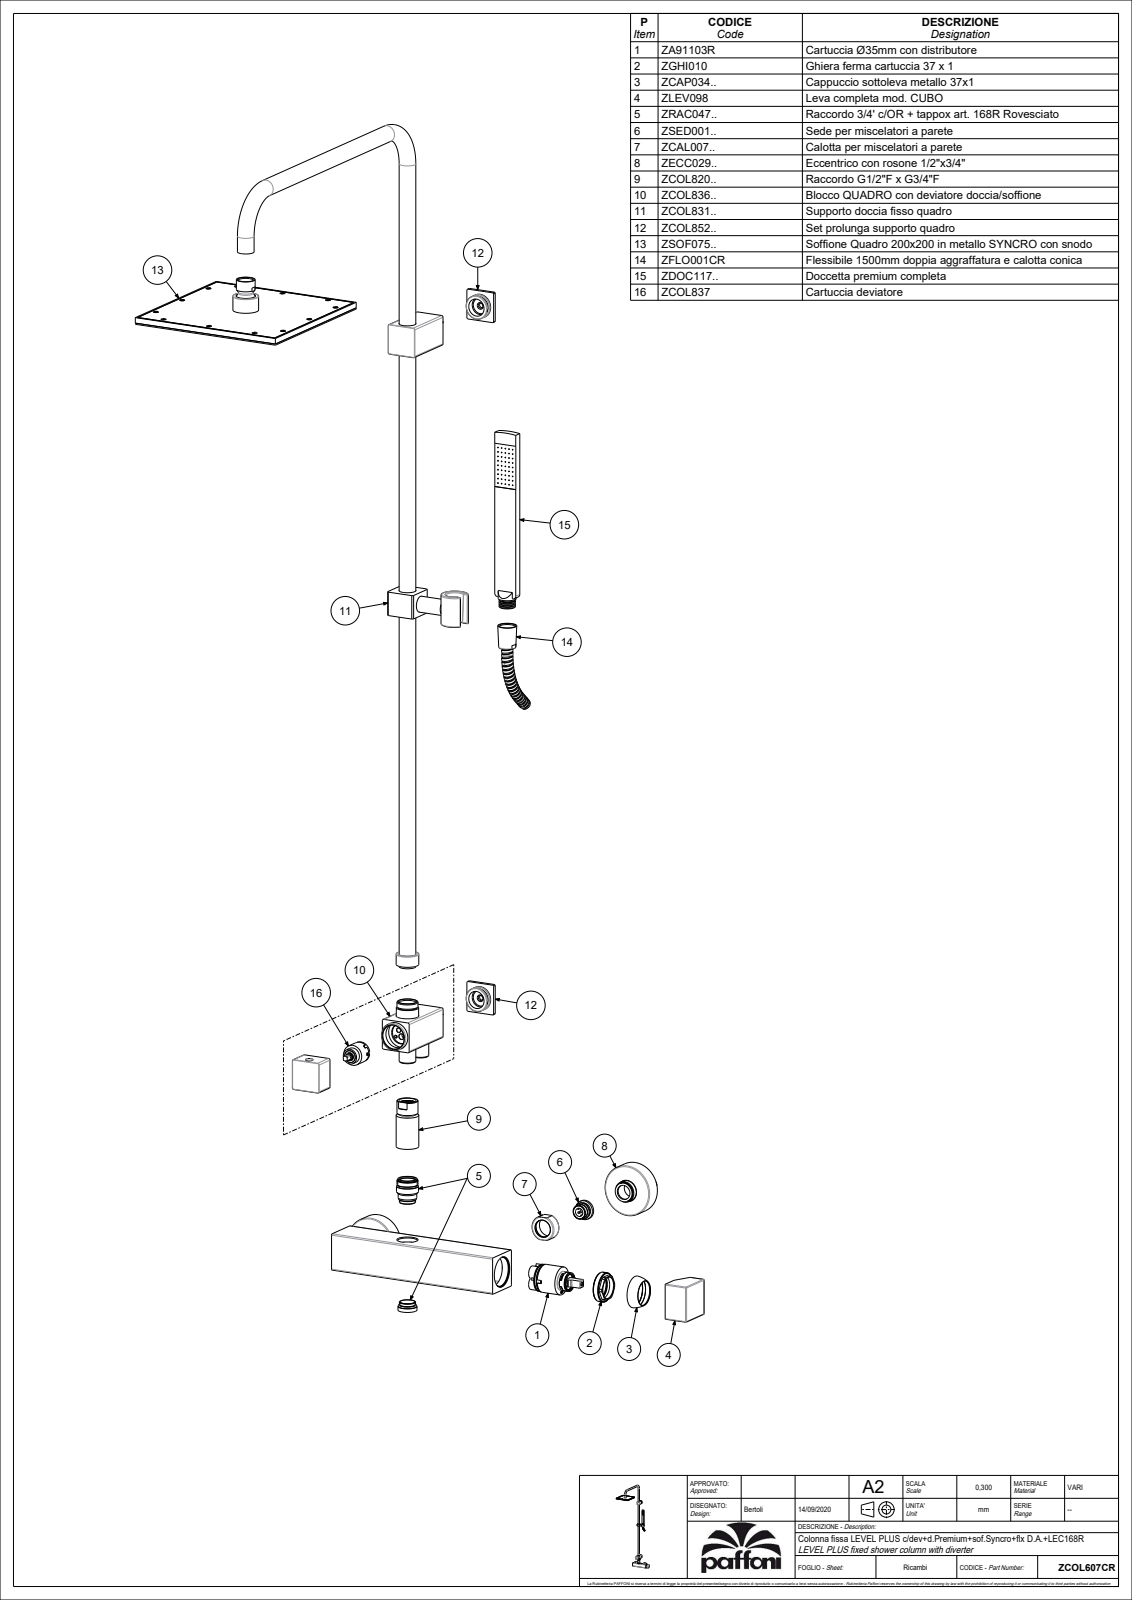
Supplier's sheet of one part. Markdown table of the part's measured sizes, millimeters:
| quantity | value |
| --- | --- |
| part name | ZCOL607CR |
| STEP written by | CREO PARAMETRIC BY PTC INC, 2020044 (CONFIG_CONTROL_DESIGN) |
| units | millimeters |
| bodies | 6 solids, 7389 faces (1662 planar, 1607 cylindrical, 4120 other) |
| overall size | 1269.8 × 559.1 × 272.75 |
| volume | 887 330 mm³ |
| surface area | 657 182 mm² |
| round holes (diameter × count) | 1.5 × 100, 1.7 × 100, 7 × 16, 6 × 14, 2.5 × 12, 5.1 × 12, 8 × 4, 9 × 4, 12 × 4, 4 × 3, 5.5 × 3, 10.5 × 3 |
| round bosses / shafts (diameter × count) | 10 × 101, 5 × 16, 2 × 11, 20.6 × 4, 63.5 × 2, 29.7 × 2, 27 × 2, 24 × 2 |
| partial cylindrical surfaces (radius × count) | 1 × 114, 0.5 × 66, 0.3 × 57, 0.2 × 12, 20 × 12, 0.15 × 11, 2 × 10, 1.5 × 8 |
| main face-to-face distances | 8.5, 7.5, 1, 42.75, 3.75, 7, 1.5, 6, 46.5, 39 |
| hole center spacings | 16.3, 36.45, 23.05, 51.55, 32.6, 67.21, 48.9, 83.11 |
